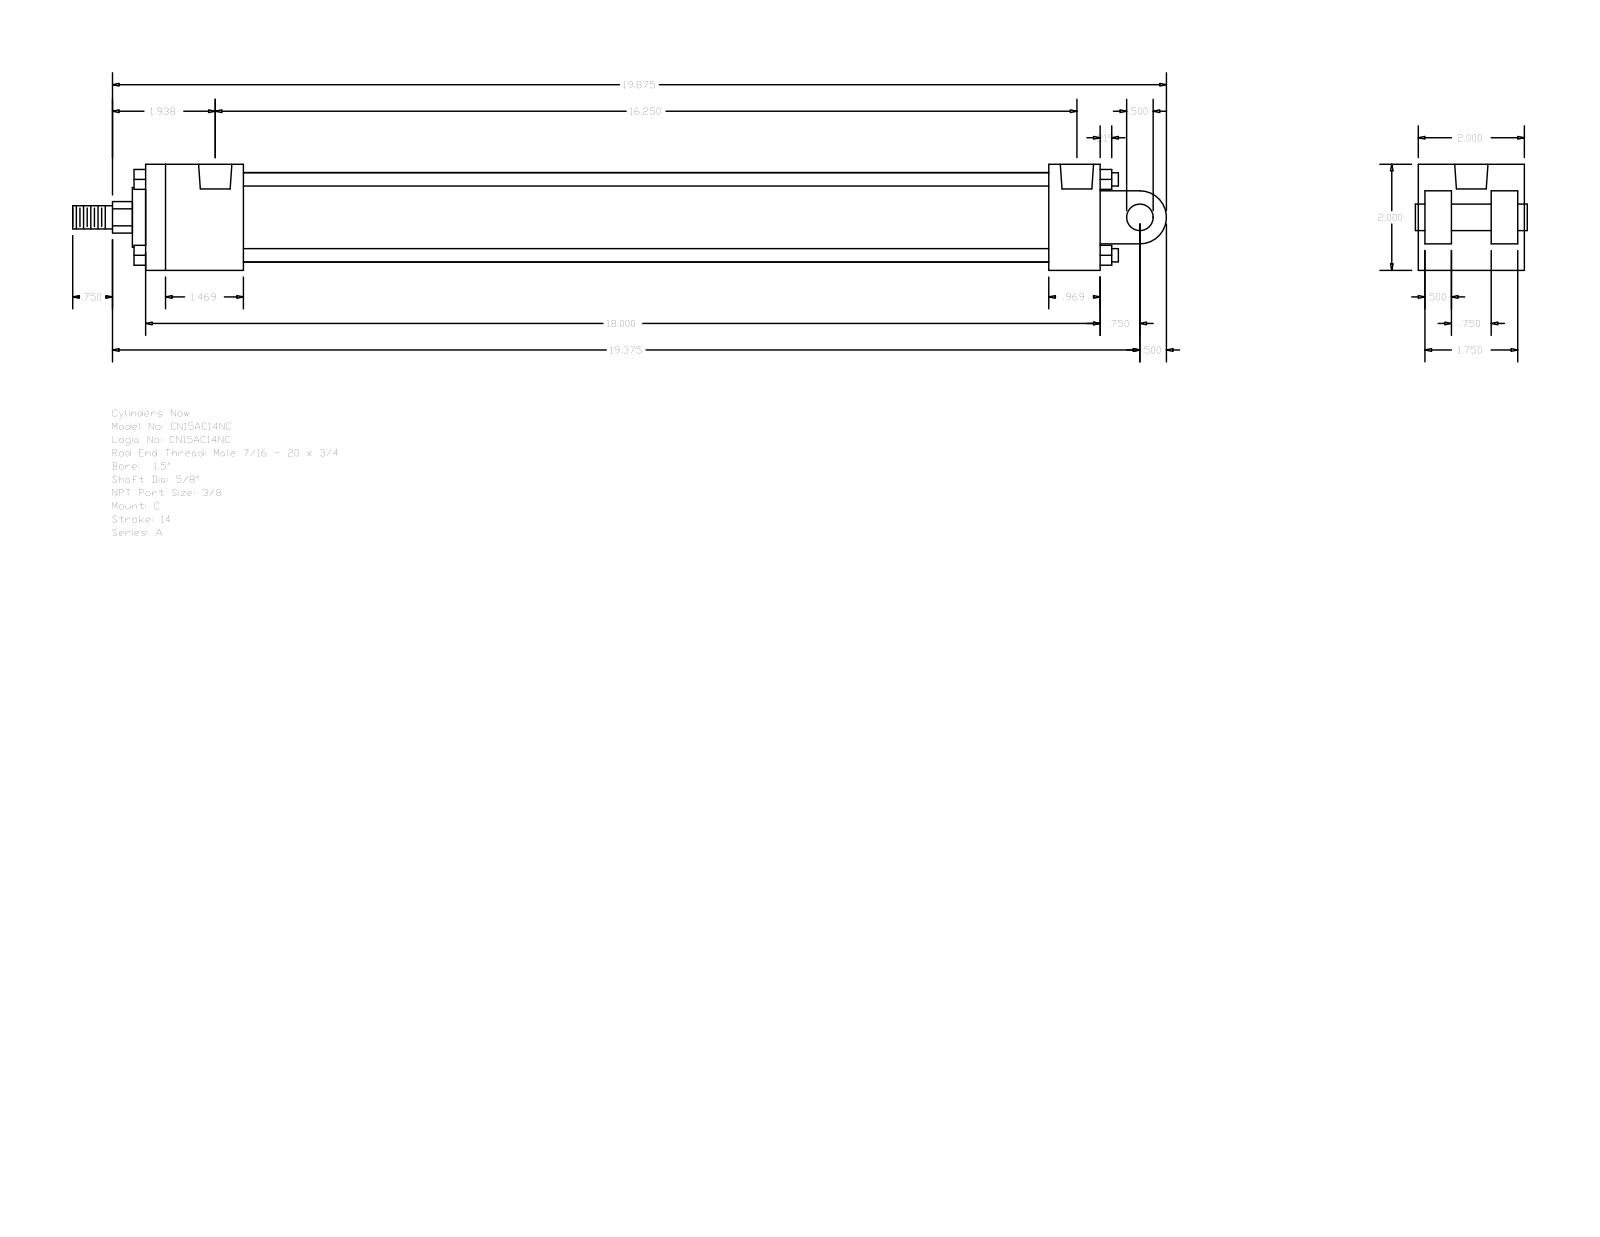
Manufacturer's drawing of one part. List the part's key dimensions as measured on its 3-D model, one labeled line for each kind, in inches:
Part name (STEP PRODUCT): A_C__0150_0.625
STEP written by: GSSL Pune (CONFIG_CONTROL_DESIGN)
Units: inches
Bodies: 0 solids, 135 faces (102 planar, 33 cylindrical, 0 other)
Overall size (bounding box): 20.625 × 2 × 2
Round holes (diameter × count): ⌀0.219 ×4, ⌀0.627 ×2
Round bosses / shafts (diameter × count): ⌀0.25 ×4, ⌀1.69 ×1, ⌀1.125 ×1, ⌀0.625 ×1, ⌀0.5 ×1, ⌀0.437 ×1
Partial cylindrical surfaces — rounded edges, fillets, slot ends (radius × count): R0.297 ×1, R0.5 ×1
Main face-to-face distances: 2, 0.5, 18, 1.375, 0.125, 0.625, 1.875, 1.25, 17.031, 0.969
Hole centre spacings: 0.156, 15.937, 16.094, 16.25
